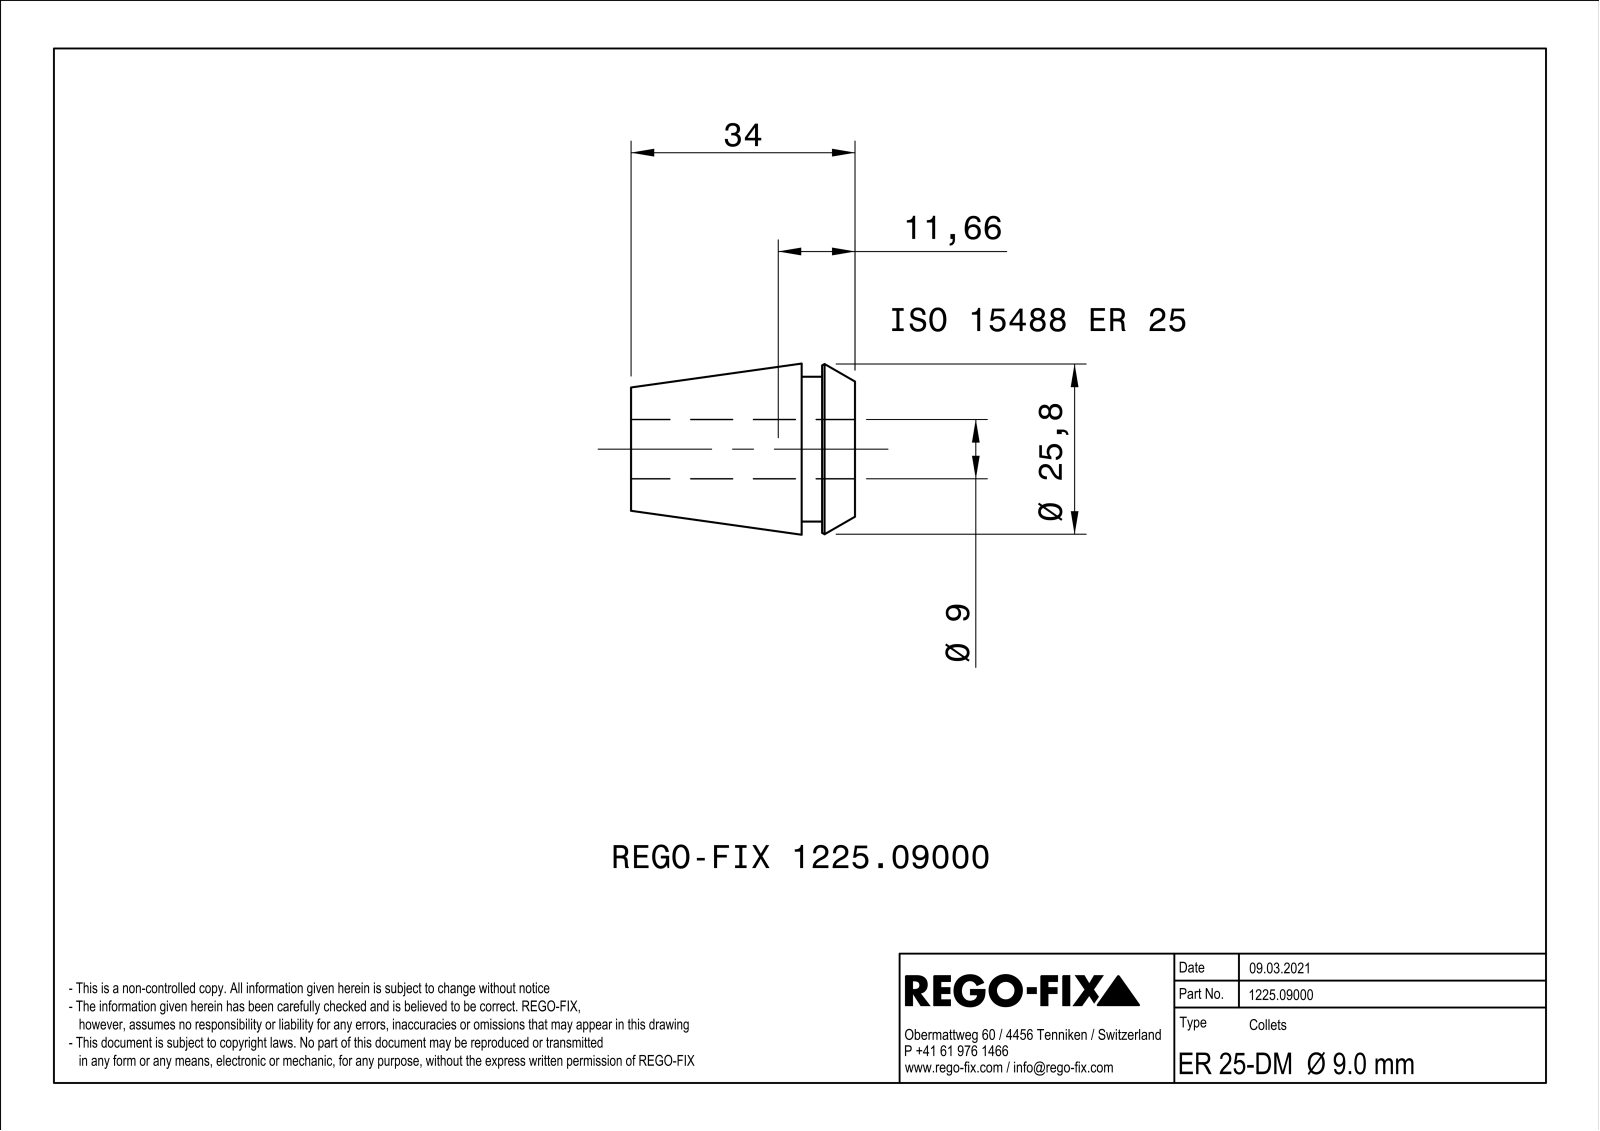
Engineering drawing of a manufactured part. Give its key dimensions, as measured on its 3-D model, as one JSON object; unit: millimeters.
{"part_name": "NOCUT", "step_written_by": "SIEMENS PLM Software Solid Edge ST10 (AUTOMOTIVE_DESIGN)", "units": "millimeters", "bodies": {"solids": 1, "faces": 154, "planar": 80, "cylindrical": 9, "other": 65}, "overall_size": [34, 25.99, 25.99], "volume_mm3": 9378, "surface_area_mm2": 8683, "round_holes": [[9, 1]], "round_bosses_or_shafts": [[22, 1]], "face_to_face_distances": [0.8, 34, 5, 29, 8.1, 25.9, 3.1, 15, 10, 6.9]}
